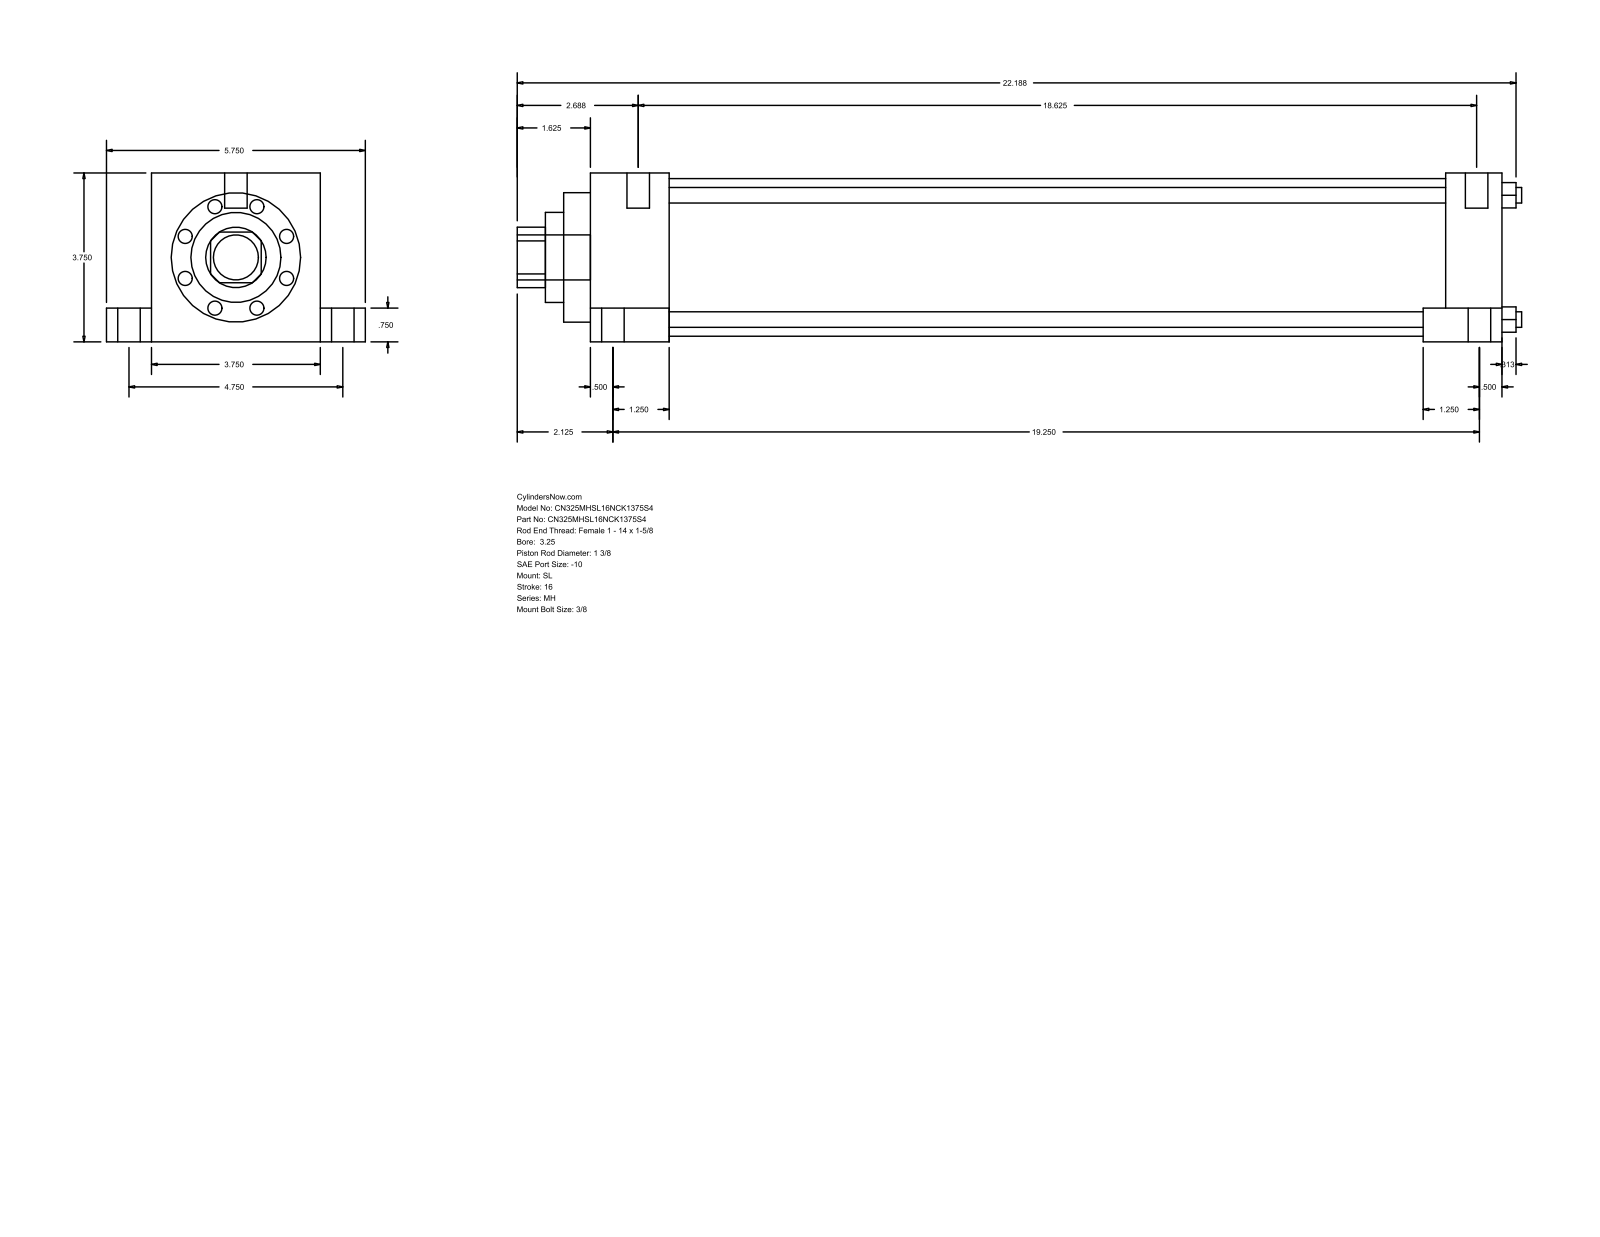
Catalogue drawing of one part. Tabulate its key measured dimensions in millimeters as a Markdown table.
| quantity | value |
| --- | --- |
| part name | MH_SL__0325_1.375 |
| STEP written by | GSSL Pune (CONFIG_CONTROL_DESIGN) |
| units | millimeters |
| bodies | 0 solids, 110 faces (77 planar, 33 cylindrical, 0 other) |
| overall size | 566.74 × 146.05 × 95.25 |
| round holes (diameter × count) | 8.76 × 4, 34.92 × 1, 50.8 × 1, 73.03 × 1, 88.9 × 1 |
| round bosses / shafts (diameter × count) | 12.7 × 6, 19.05 × 4, 5.56 × 4, 25.4 × 1 |
| partial cylindrical surfaces (radius × count) | 17.06 × 1 |
| main face-to-face distances | 95.24, 514.35, 44.45, 469.9, 25.41, 120.65, 19.05, 76.19, 482.61, 438.16 |
| hole center spacings | 49.57, 70.1, 99.14 |
